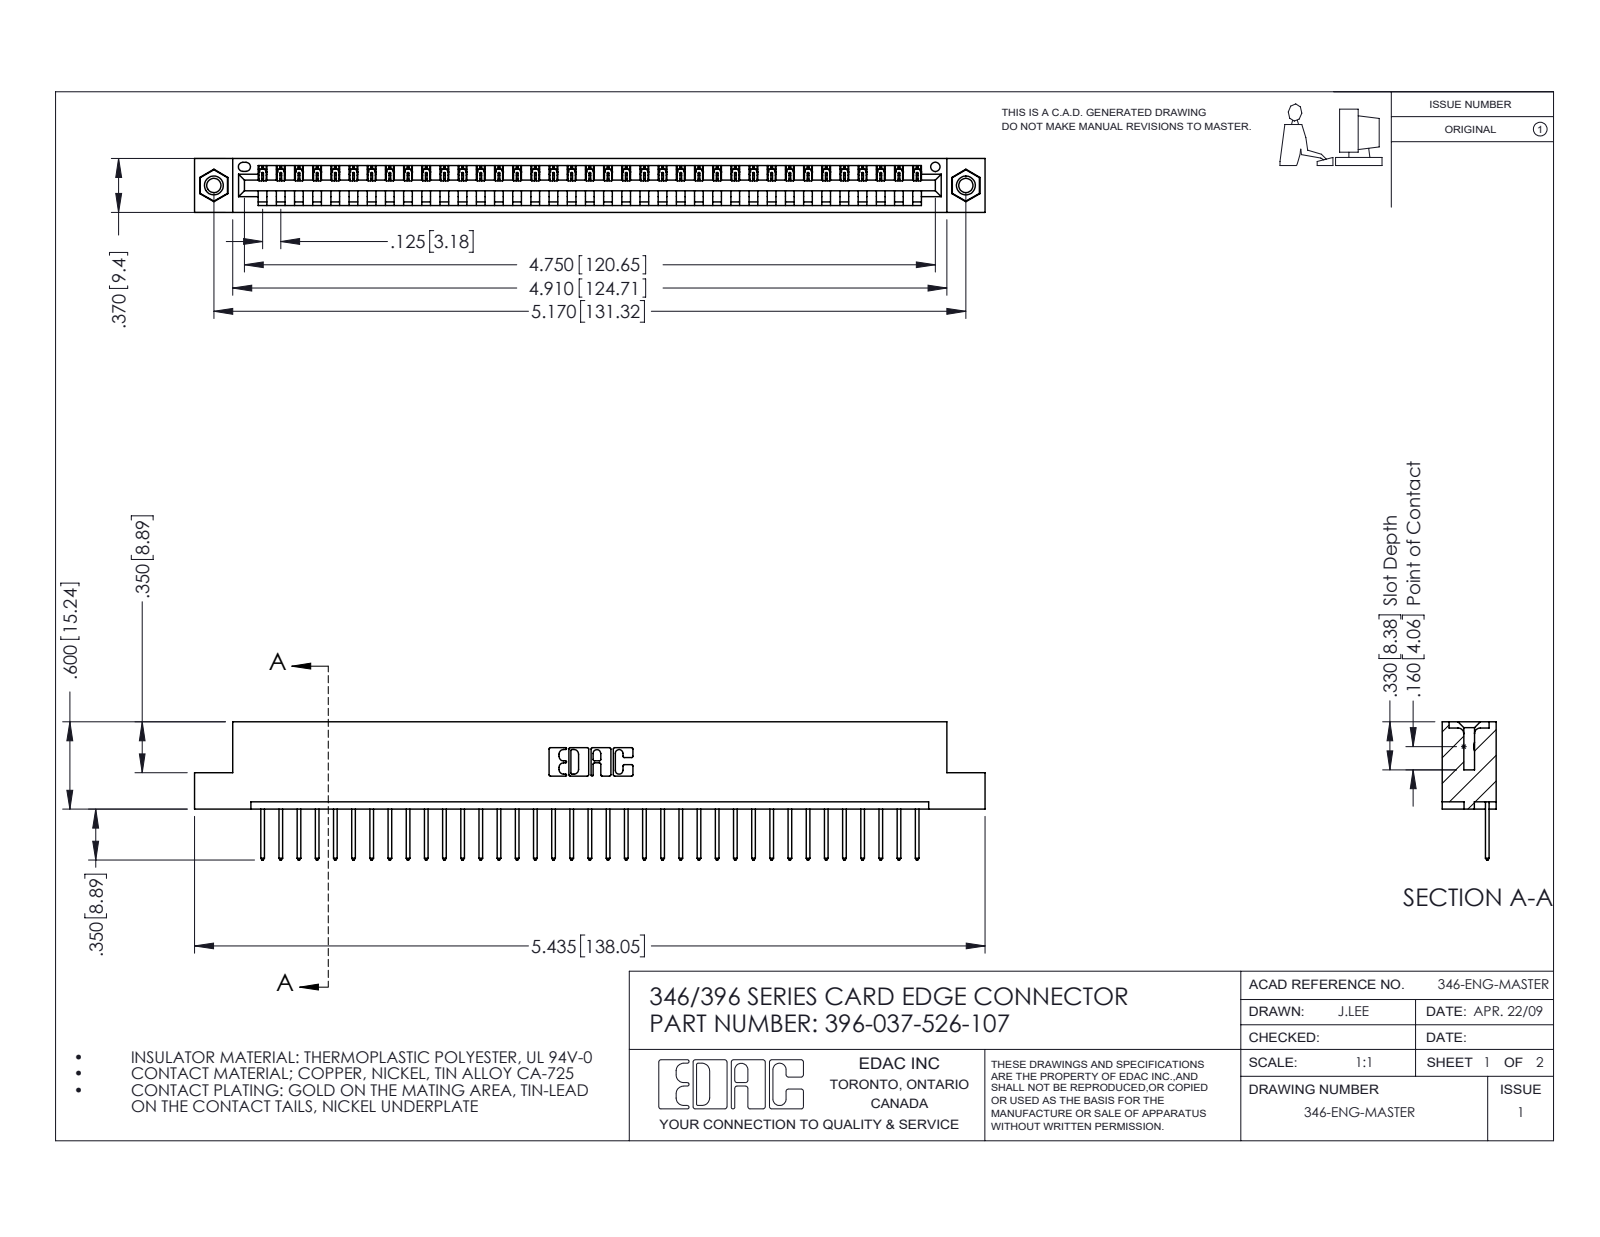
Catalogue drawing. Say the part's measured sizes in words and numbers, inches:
The part is named "345-250-001_345-250-005-103; 345-292-001_345-293-126; 346 Part_Flush Mounting Lugs - 0.156 Dia-TI; 396-037-526-107". Its 3-D file was written by "SolidWorks 2016 (CONFIG_CONTROL_DESIGN)". It is 40 solids with 2328 faces: 1588 planar, 724 cylindrical and 16 other. Overall it measures 5.435 by 0.95 by 0.37 inches. Its volume is 0.802 cubic inches and its surface area 25.36 square inches. Round holes: 2 of diameter 0.098, 2 of diameter 0.125, 2 of diameter 0.156, 1 of diameter 0.064. Round bosses or shafts: 2 of diameter 0.155. Partial cylindrical surfaces (rounded edges, fillets, slot ends): 74 of radius 0.006, 74 of radius 0.01, 22 of radius 0.01, 6 of radius 0.007, 6 of radius 0.031, 3 of radius 0.026, 2 of radius 0.031, 2 of radius 0.04. The main face-to-face distances are 0.048, 0.322, 0.37, 0.25, 0.072, 0.298, 0.025, 0.148, 0.222, 0.1. The hole center spacings are 0.246, 4.961, 5.17.
